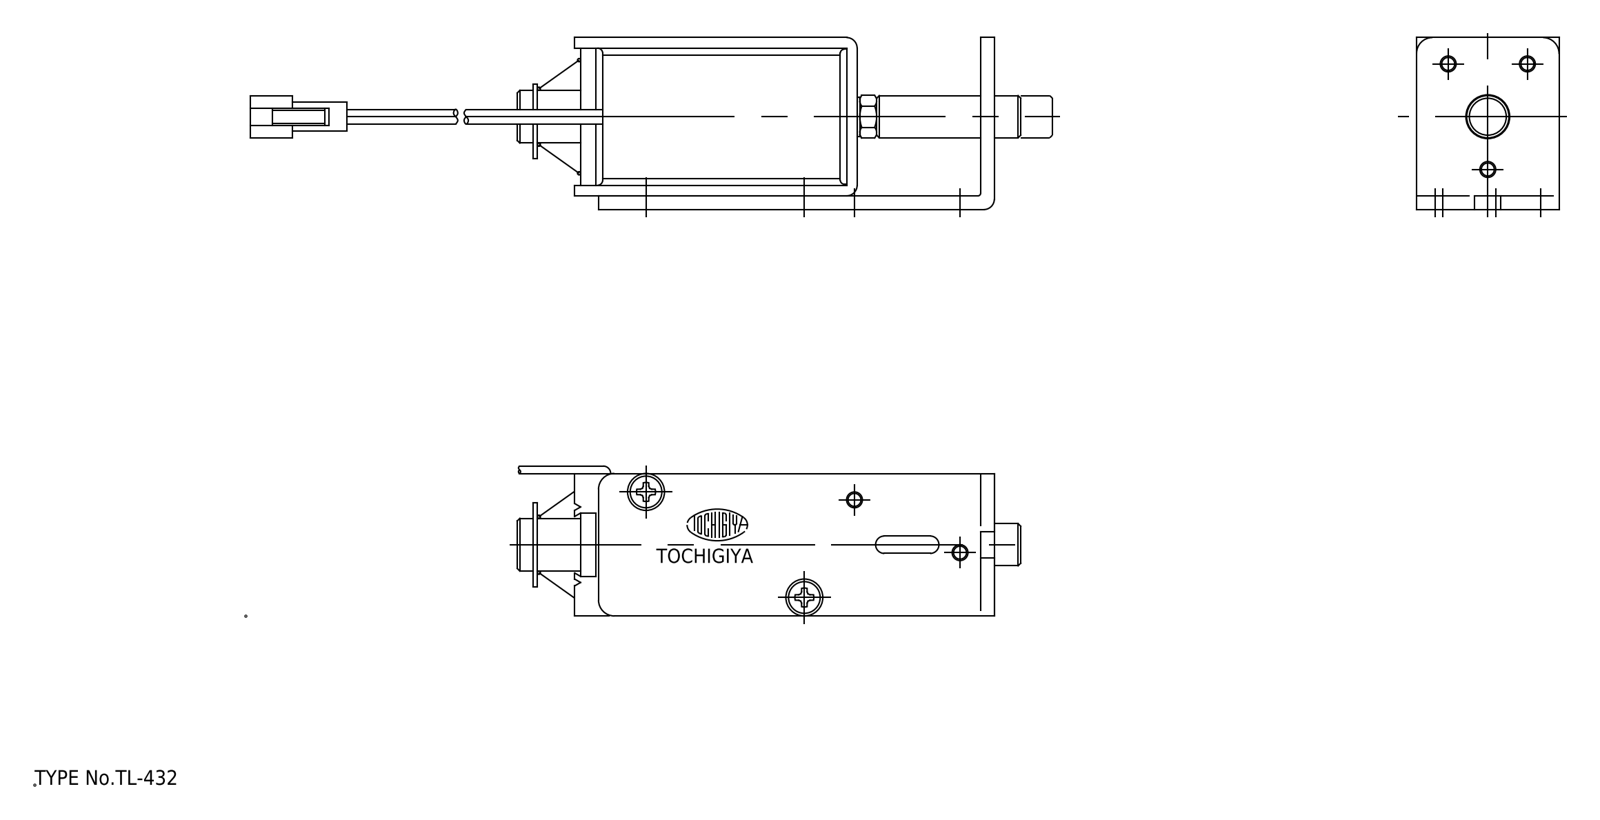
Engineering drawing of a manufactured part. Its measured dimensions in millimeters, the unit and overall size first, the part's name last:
Units: millimetres
Overall size (bounding box): 145.94 × 33.15 × 32.6
Round holes (diameter × count): ⌀3 ×9, ⌀8.3 ×1
Round bosses / shafts (diameter × count): ⌀1.4 ×4, ⌀6 ×2, ⌀25.6 ×1, ⌀23.4 ×1, ⌀10 ×1, ⌀8 ×1, ⌀7.5 ×1
Partial cylindrical surfaces — rounded edges, fillets, slot ends (radius × count): R1 ×8, R0.3 ×4, R3 ×4, R0.5 ×3, R2 ×3, R1.65 ×2, R6.2 ×1, R8 ×1
Main face-to-face distances: 28, 2, 26, 2.6, 32.6, 4.6, 30.6, 30, 75.8, 78.4
Hole centre spacings: 12.5, 20, 21.36, 30, 36.06, 9.62, 10, 15
Bodies: 0 solids, 346 faces (213 planar, 80 cylindrical, 53 other)
STEP written by: spGate 16.7.1 (AUTOMOTIVE_DESIGN)
